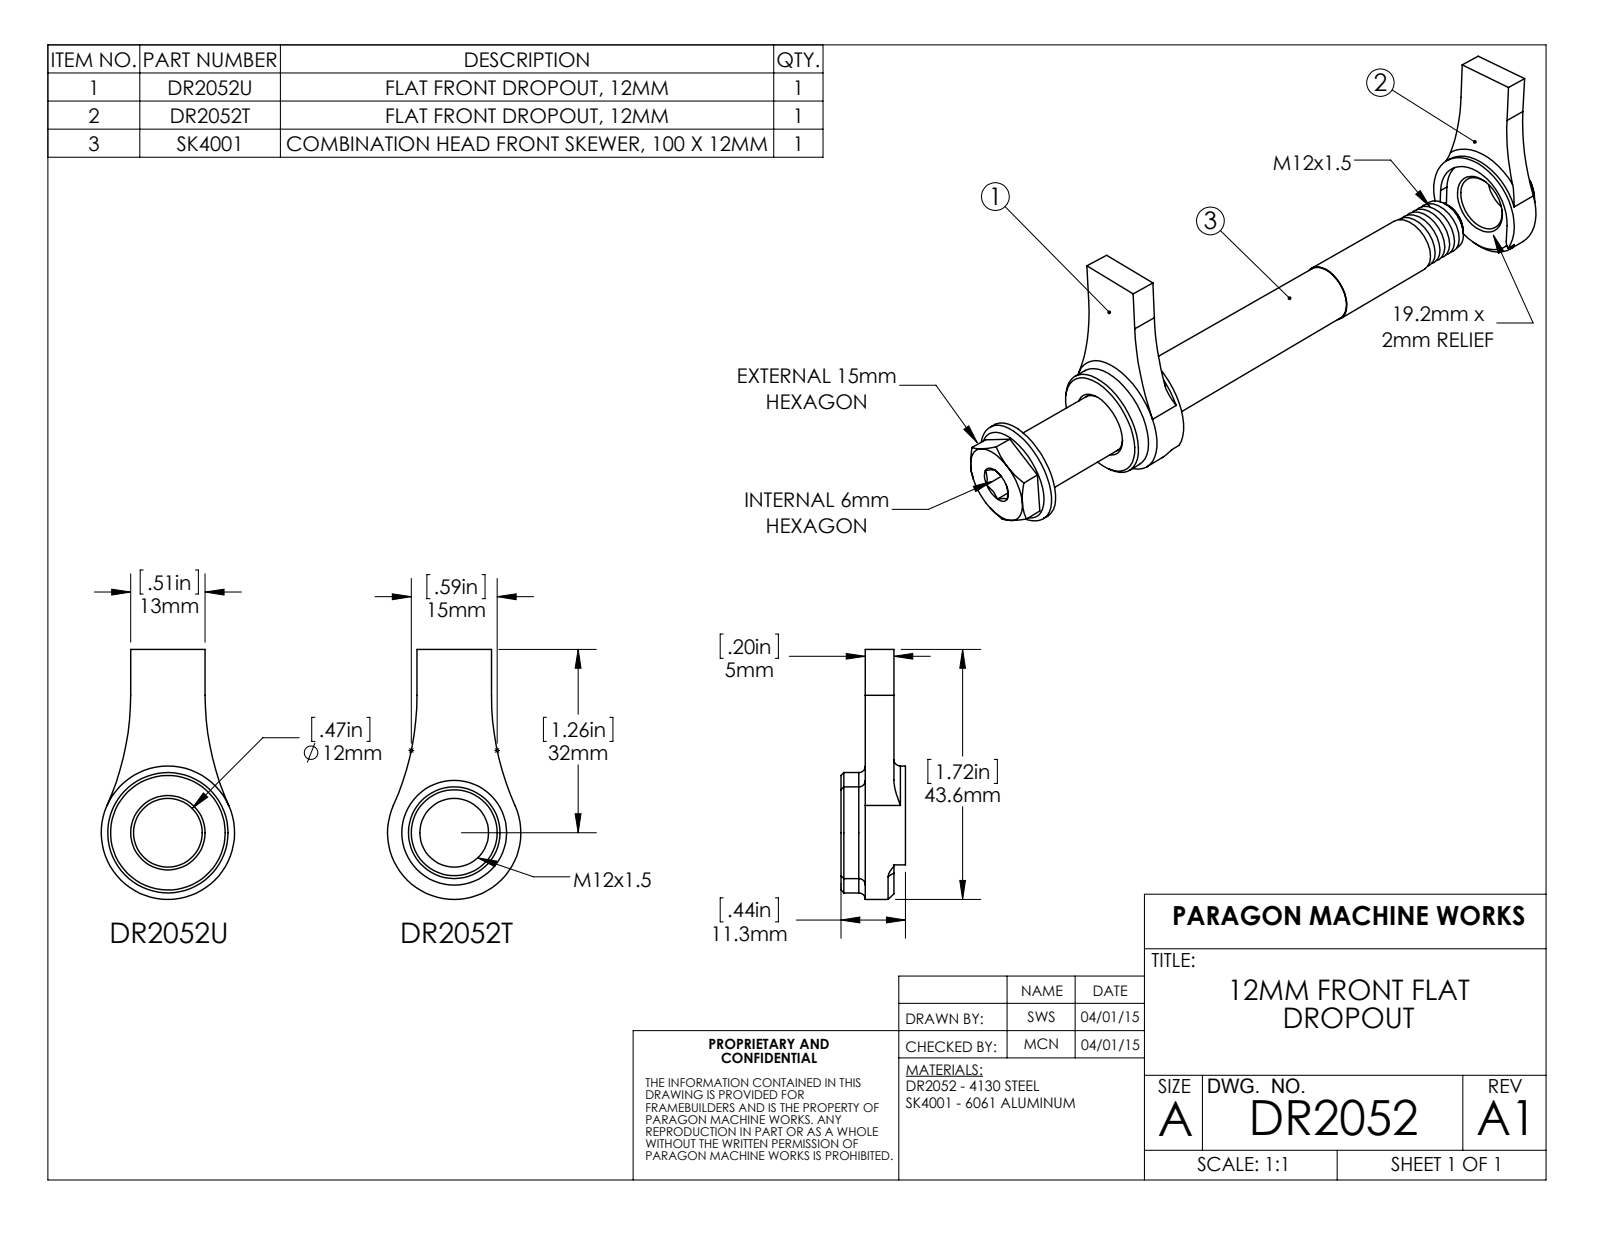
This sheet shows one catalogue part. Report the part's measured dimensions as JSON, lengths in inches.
{"part_name": "DR2052U; DR2052T; SK4001; DR2052", "step_written_by": "SolidWorks 2015 (AUTOMOTIVE_DESIGN)", "units": "inches", "bodies": {"solids": 3, "faces": 110, "planar": 40, "cylindrical": 30, "other": 40}, "overall_size": [5.689, 1.718, 0.917], "volume_in3": 1.33, "surface_area_in2": 16.62, "round_holes": [[0.472, 1]], "round_bosses_or_shafts": [[0.917, 1], [0.827, 1], [0.787, 1], [0.63, 1], [0.471, 1], [0.46, 1]], "partial_cylinders_radius": [[0.098, 2], [1.848, 2], [0.378, 1]], "face_to_face_distances": [0.197, 4.134, 3.937, 4.331, 5.089, 0.167, 0.364, 4.301, 4.498, 0.079]}
